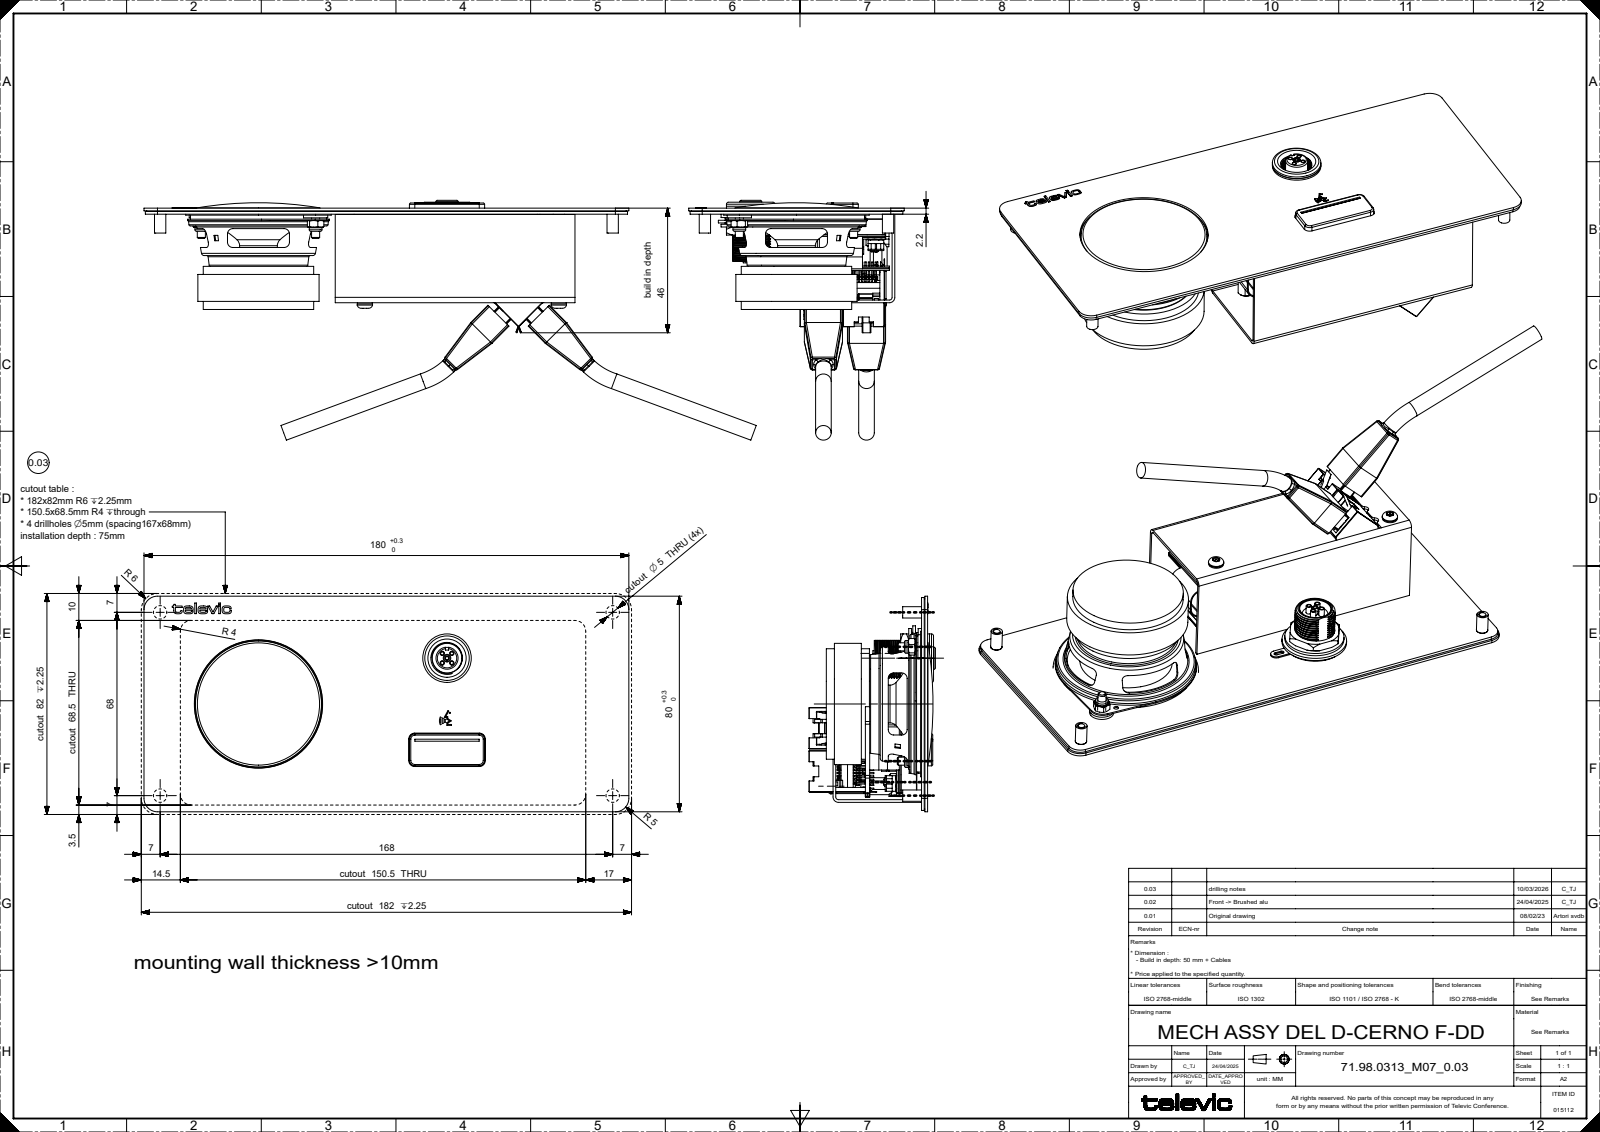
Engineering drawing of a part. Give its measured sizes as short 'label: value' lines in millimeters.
name: 3500015_VC-3500015; 3500017_VC-3500017; 3100110_VC-3100110; 310110_VC-310110 (+8 more)
written by: SIEMENS PLM Software NX 2000 (AUTOMOTIVE_DESIGN)
unit: mm
bodies: 107 solids, 4299 faces (2369 planar, 1095 cylindrical, 835 other)
size: 245.48 × 88.98 × 80
volume: 134 560 mm³; area: 219 514 mm²
holes: 6× ⌀2.44, 6× ⌀2.46, 6× ⌀3.5, 6× ⌀4.25, 5× ⌀1.4, 5× ⌀3.2, 4× ⌀3.35, 2× ⌀1.8, 2× ⌀4.2, 2× ⌀6, 1× ⌀2.8, 1× ⌀9.7
bosses: 6× ⌀4.2, 6× ⌀3.7, 6× ⌀3, 6× ⌀2.5, 5× ⌀2, 4× ⌀5.8, 4× ⌀4.6, 4× ⌀3.3
rounds: 182× R0.25, 66× R0.5, 60× R0.2, 56× R1, 26× R0.75, 16× R2.5, 15× R2, 12× R1.95
face distances: 1, 1.25, 11.6, 0.6, 20.5, 1.6, 2.25, 20.85, 22.1, 21.5
hole spacings: 2.5, 3.54, 5.01, 5.38, 28.44, 30, 49.88, 58.2
